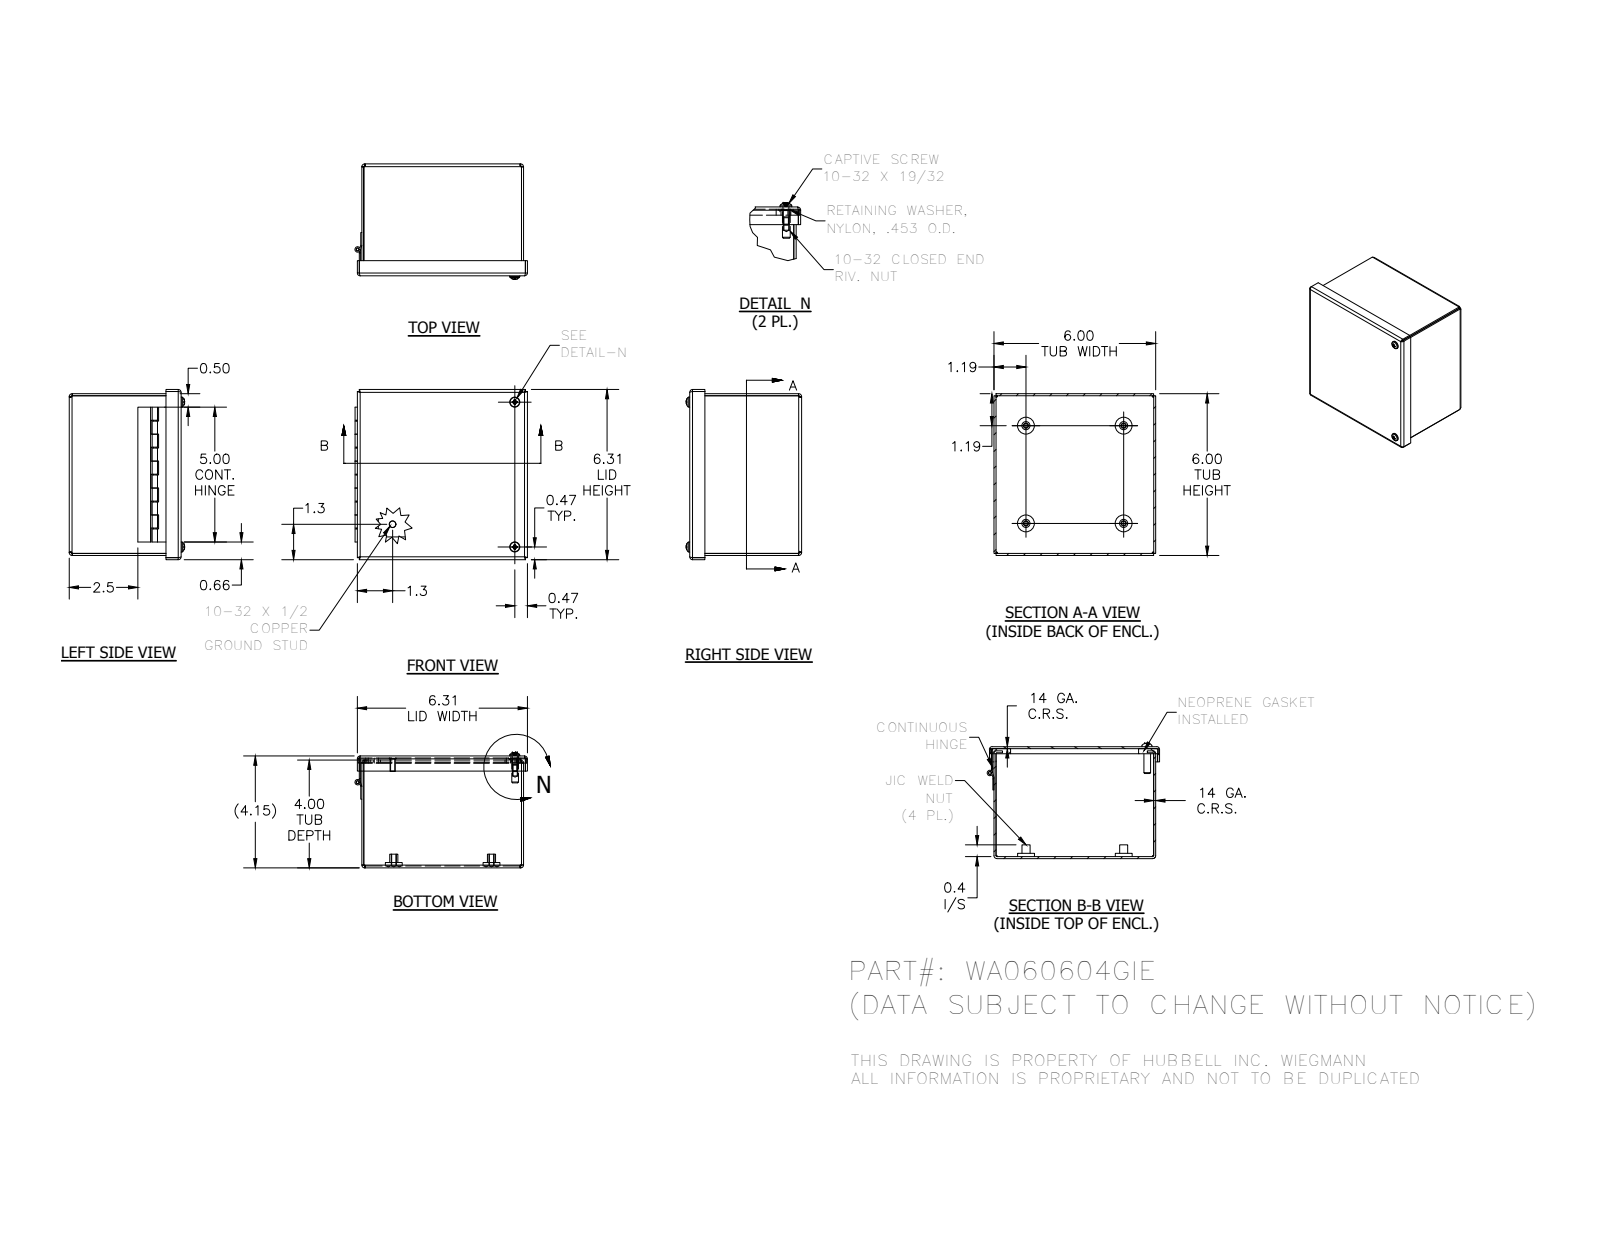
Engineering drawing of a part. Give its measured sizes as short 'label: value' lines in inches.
name: WA060604GIEBKP; 3499; 328120LH; 328120P (+8 more)
written by: Autodesk Inventor 2014 (AUTOMOTIVE_DESIGN)
unit: in
bodies: 18 solids, 425 faces (245 planar, 105 cylindrical, 75 other)
size: 6.397 × 6.313 × 4.282
volume: 17.32 in³; area: 445.5 in²
holes: 6× ⌀0.156, 4× ⌀0.257, 4× ⌀0.313, 2× ⌀0.196, 2× ⌀0.278, 2× ⌀0.281, 1× ⌀0.117
bosses: 4× ⌀0.625, 4× ⌀0.3, 3× ⌀0.19, 2× ⌀0.453, 2× ⌀0.406, 2× ⌀0.373, 2× ⌀0.248, 1× ⌀0.25
rounds: 12× R0.031, 12× R0.105, 8× R0.07, 2× R0.089
face distances: 0.074, 5.926, 4.078, 6, 5.852, 4.004, 4.152, 0.187, 0.261, 3.891
hole spacings: 5.375, 4.584, 1.237, 6.364, 3.625, 5.374, 5.386, 7.601
